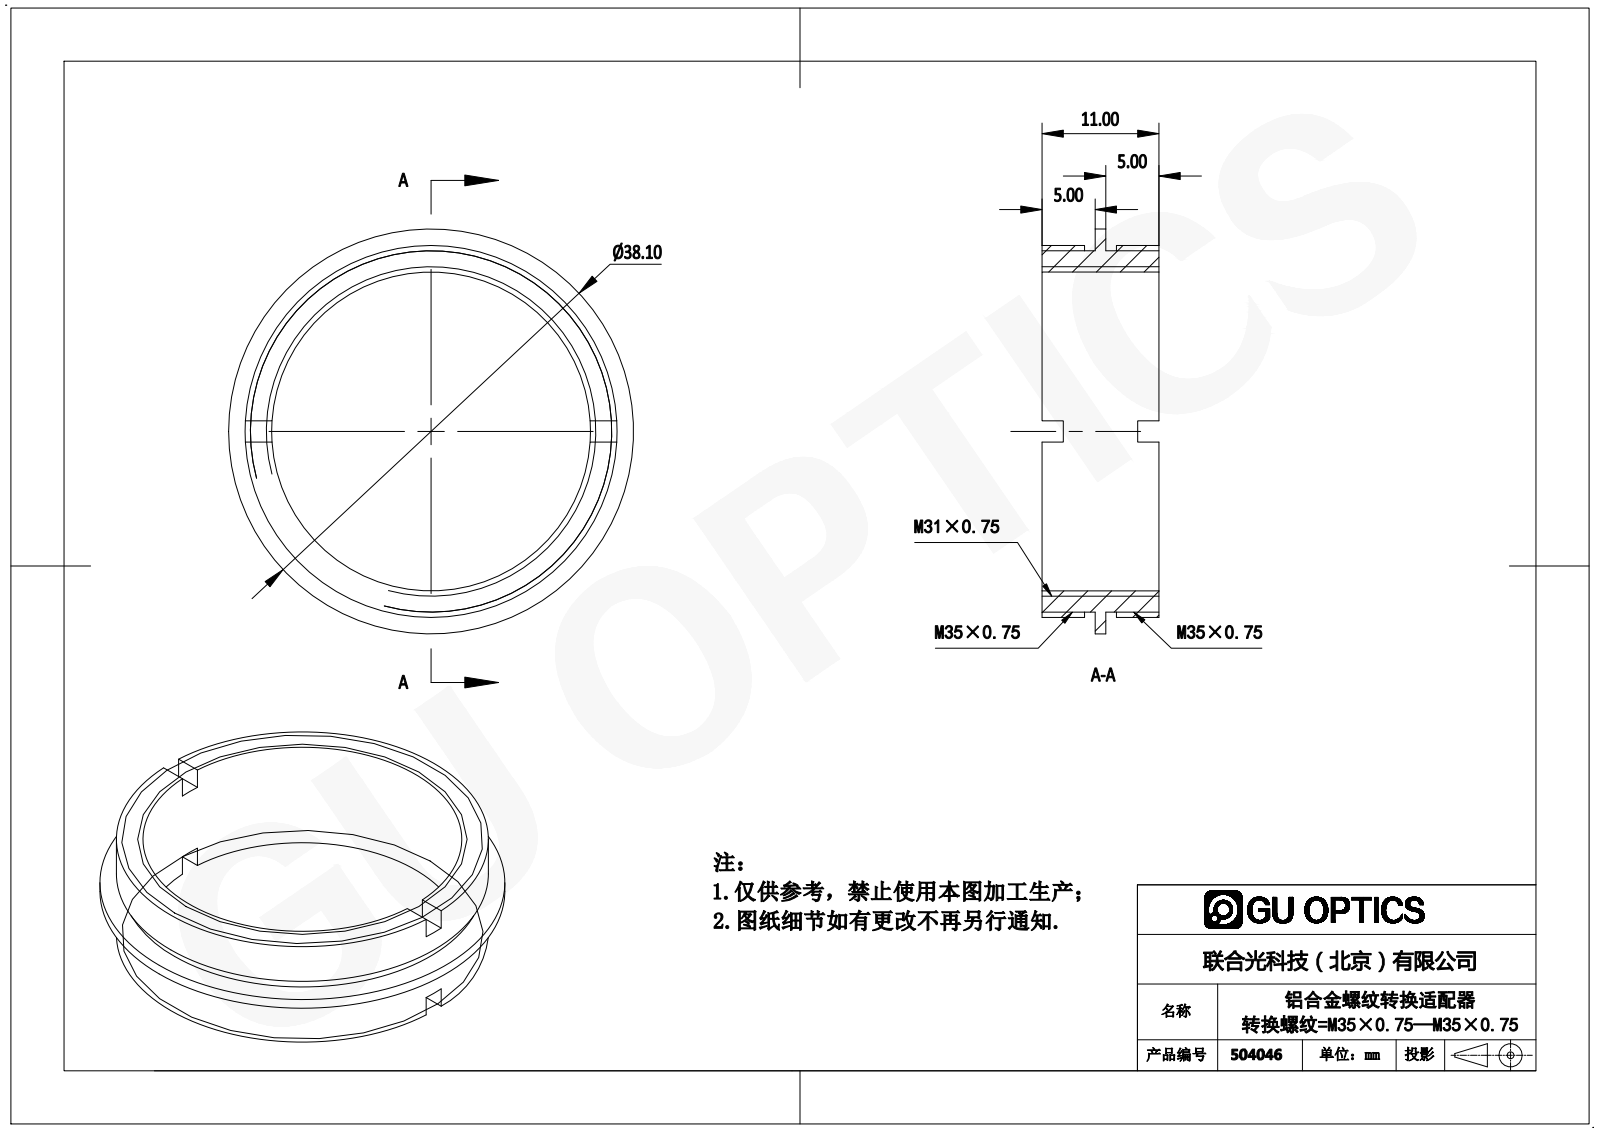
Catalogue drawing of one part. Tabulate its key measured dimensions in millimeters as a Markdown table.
| quantity | value |
| --- | --- |
| part name | 504046 |
| STEP written by | SolidWorks 2016 (AUTOMOTIVE_DESIGN) |
| units | millimeters |
| bodies | 1 solid, 32 faces (20 planar, 12 cylindrical, 0 other) |
| overall size | 38.1 × 38.1 × 11 |
| volume | 2 837 mm³ |
| surface area | 3 341 mm² |
| round holes (diameter × count) | 30 × 1 |
| round bosses / shafts (diameter × count) | 38.1 × 1, 35 × 1, 34 × 1 |
| main face-to-face distances | 5, 6, 1, 11, 2, 4, 7, 3, 9 |
